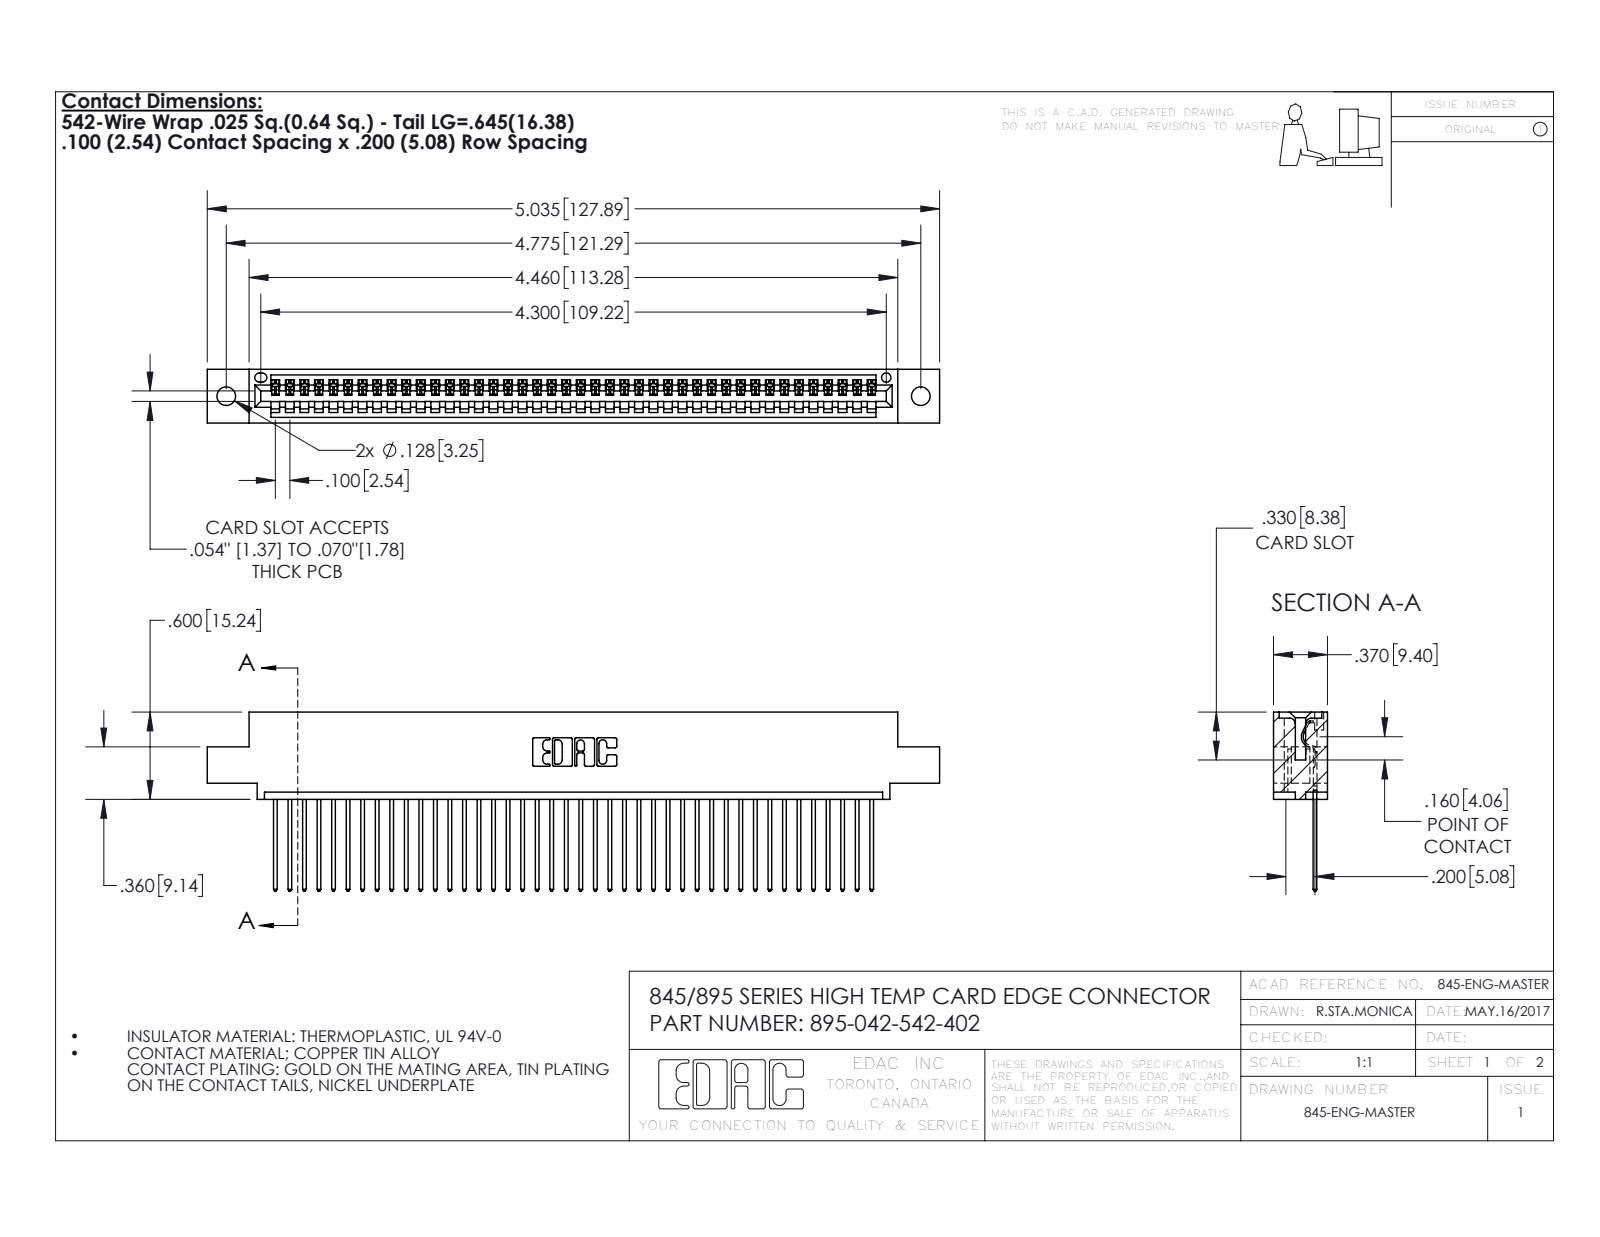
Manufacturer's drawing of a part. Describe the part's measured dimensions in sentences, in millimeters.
The part is named "345-292-001_345-293-142; 395-042-542-402; 345 Part_0.110 Offset - 0.128 Dia". Its 3-D file was written by "SolidWorks 2016 (CONFIG_CONTROL_DESIGN)". It is 43 solids with 2566 faces: 1764 planar, 802 cylindrical and 0 other. Overall it measures 127.9 by 31.3 by 9.4 millimeters. Its volume is 12 100 cubic millimeters and its surface area 16 520 square millimeters. Round holes: 2 of diameter 3.3, 1 of diameter 1.6. Partial cylindrical surfaces (rounded edges, fillets, slot ends): 84 of radius 0.2, 84 of radius 0.3, 22 of radius 0.3, 6 of radius 0.2, 6 of radius 0.8, 3 of radius 0.7, 2 of radius 0.8, 2 of radius 1. The main face-to-face distances are 1.8, 7.6, 9.4, 2.5, 6.9, 0.6, 5.1, 5.7, 3.8, 1.8. The hole center spacings are 6.9, 115.3, 121.3.
